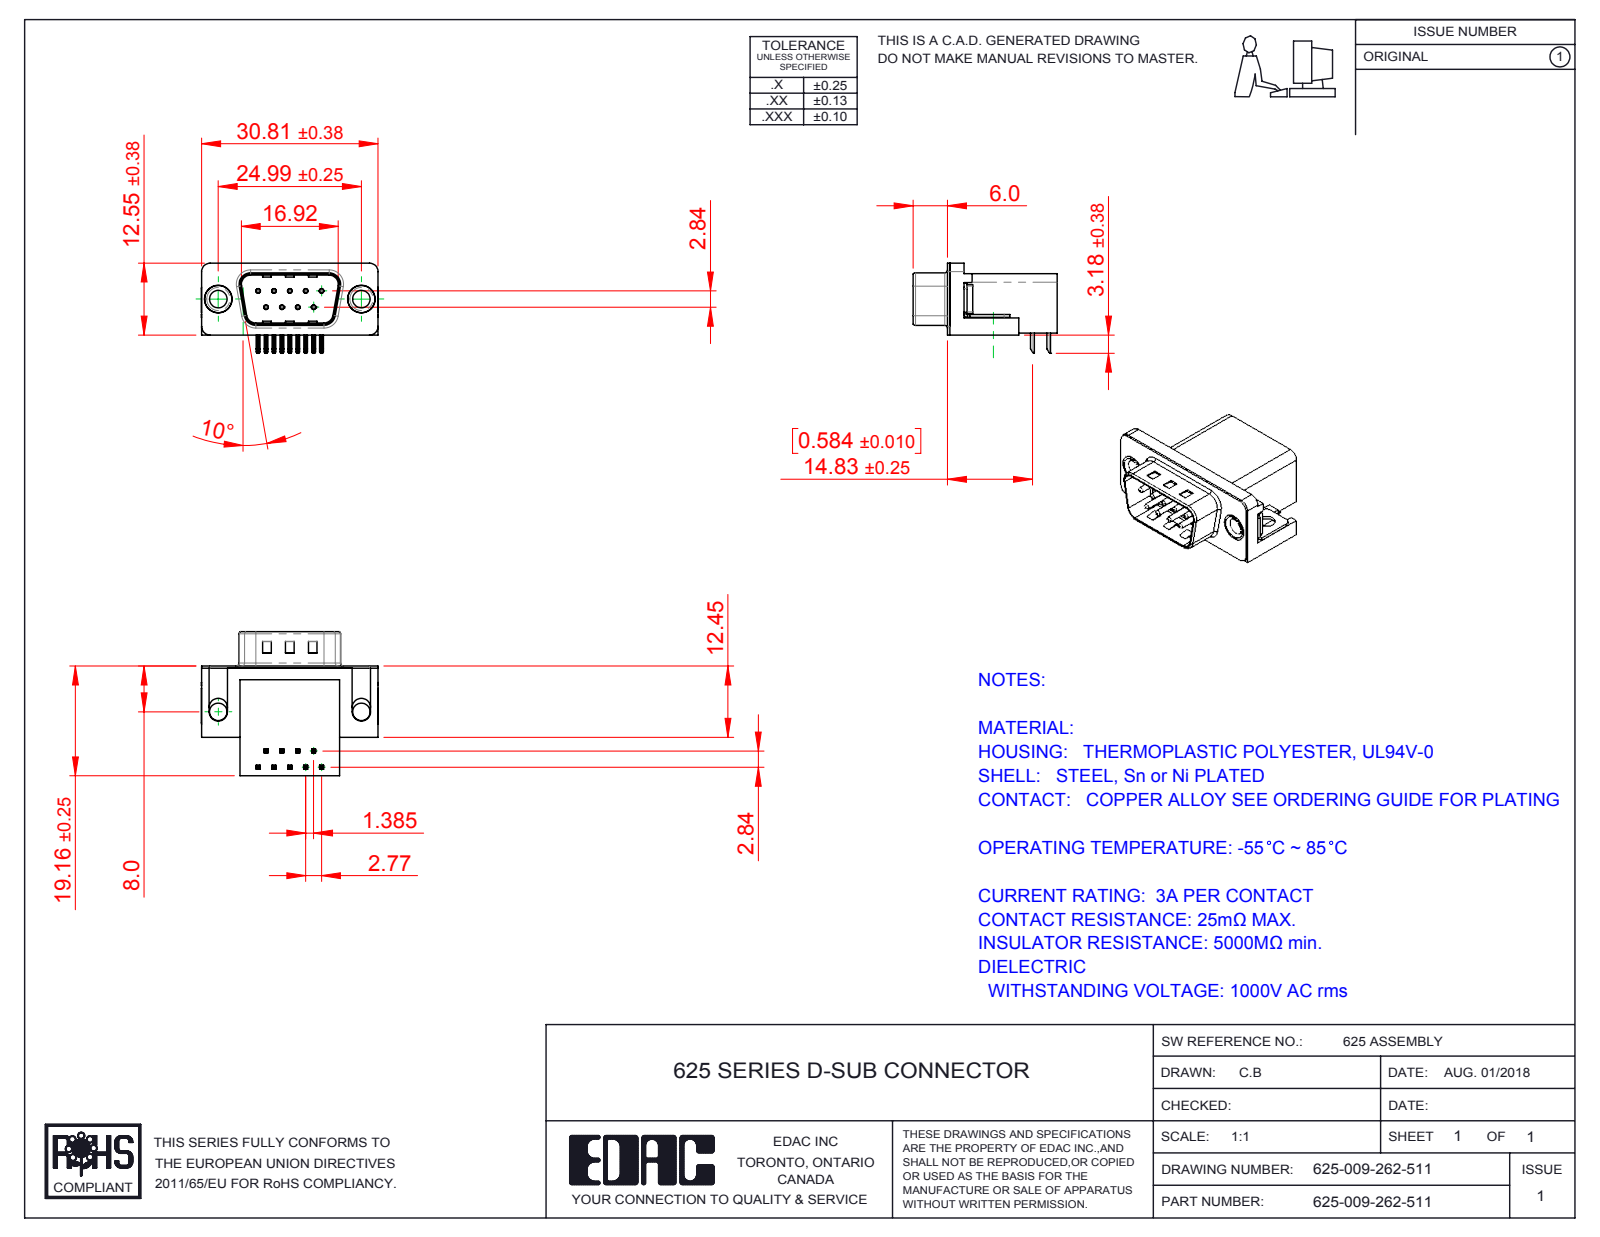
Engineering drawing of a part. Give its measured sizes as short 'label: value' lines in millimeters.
name: 625 Housing_9 Socket; 625 Shell_9 Socket; 625 Thru Hole Rivet; 625 Contact Top (+3 more)
written by: SolidWorks 2016 (CONFIG_CONTROL_DESIGN)
unit: mm
bodies: 15 solids, 953 faces (573 planar, 299 cylindrical, 81 other)
size: 30.89 × 25.16 × 15.73
volume: 4 461 mm³; area: 4 915 mm²
holes: 9× ⌀0.35, 9× ⌀0.8, 4× ⌀3.05, 2× ⌀4, 2× ⌀4.8, 2× ⌀5
bosses: 9× ⌀0.75, 2× ⌀4.9, 2× ⌀4.75, 2× ⌀3.85
rounds: 44× R0.25, 18× R0.12, 16× R1, 9× R0.5, 8× R1.5, 8× R1.6, 4× R0.9, 4× R2
face distances: 0.4, 10.34, 18.76, 19.16, 2.9, 16.26, 2.5, 0.5, 0.35, 10.69
hole spacings: 3.16, 2.77, 5.54, 5.03, 5.04, 8.31, 7.48, 7.49
